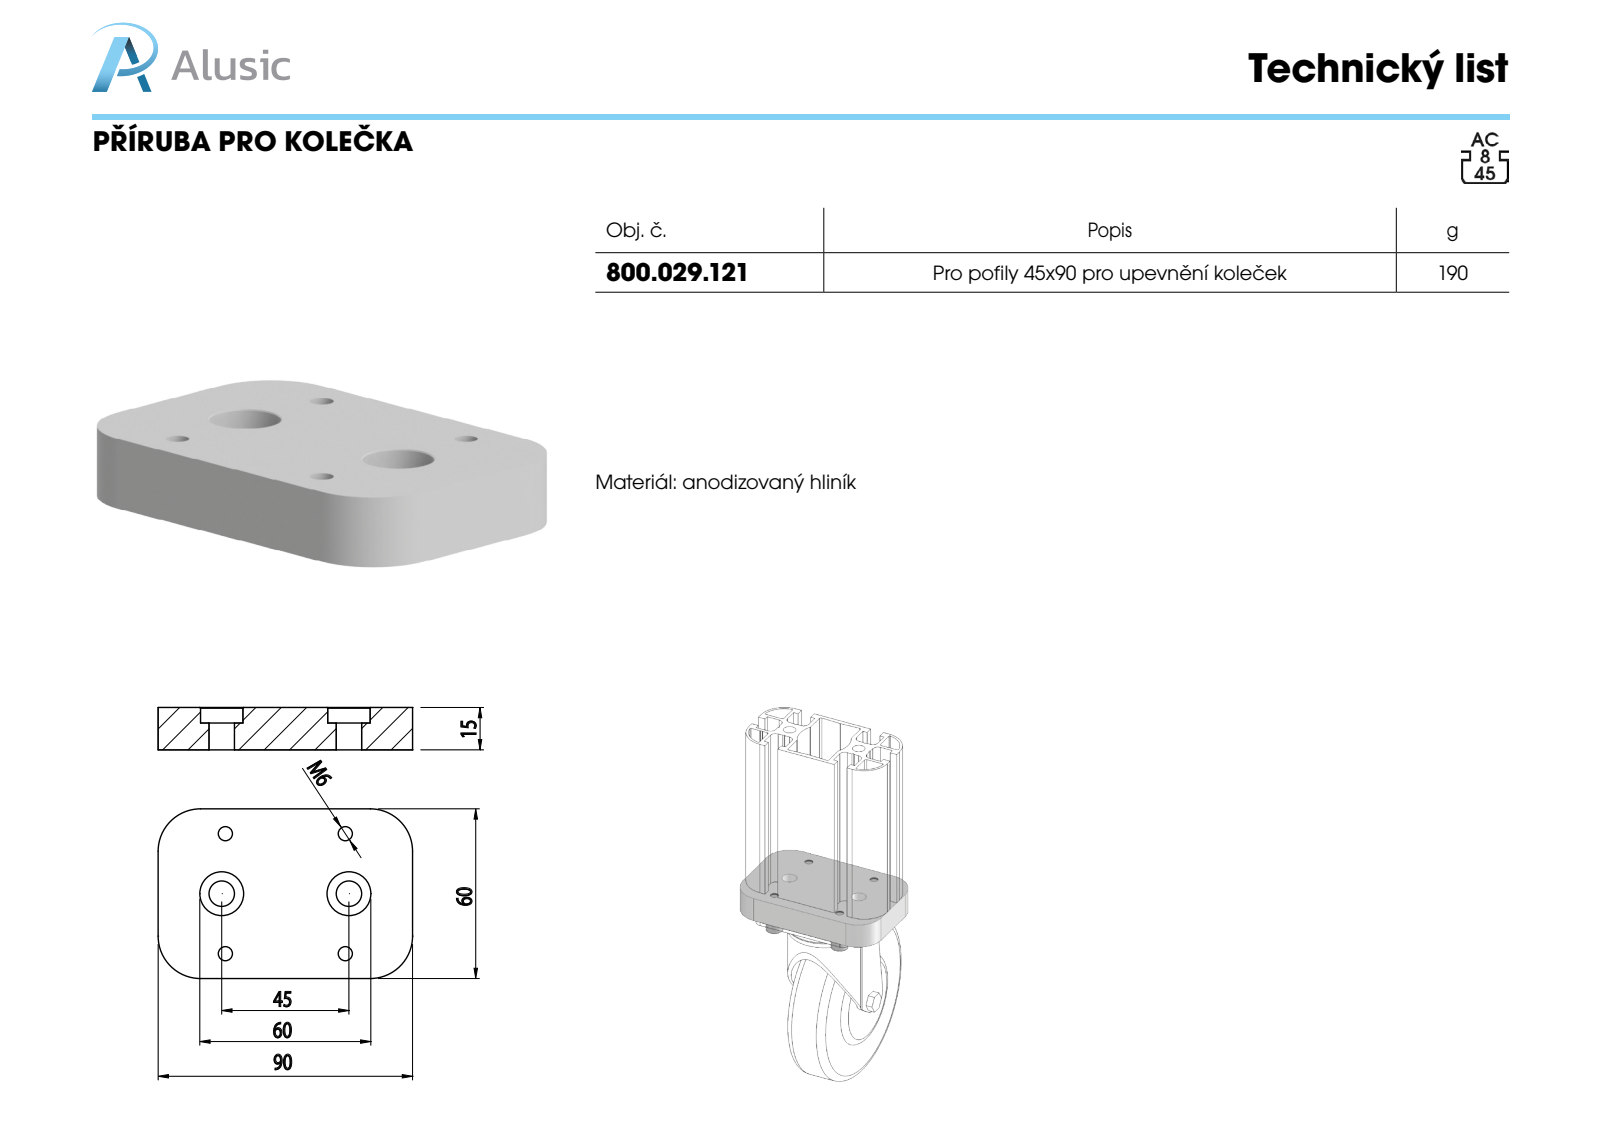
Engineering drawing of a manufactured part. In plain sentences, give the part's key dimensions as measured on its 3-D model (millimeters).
The part is named "800.029.121". Its 3-D file was written by "SolidWorks 2011 (CONFIG_CONTROL_DESIGN)". It is 1 solid with 32 faces: 8 planar, 20 cylindrical and 4 other. Overall it measures 90 by 60 by 15 millimeters. Its volume is 73 769 cubic millimeters and its surface area 16 100 square millimeters. Round holes: 4 of diameter 5, 2 of diameter 9, 2 of diameter 15. Partial cylindrical surfaces (rounded edges, fillets, slot ends): 4 of radius 15. The main face-to-face distances are 15, 60, 90, 9.5, 5.5. The hole center spacings are 21.25, 42.42, 48.58, 59.99, 45.
